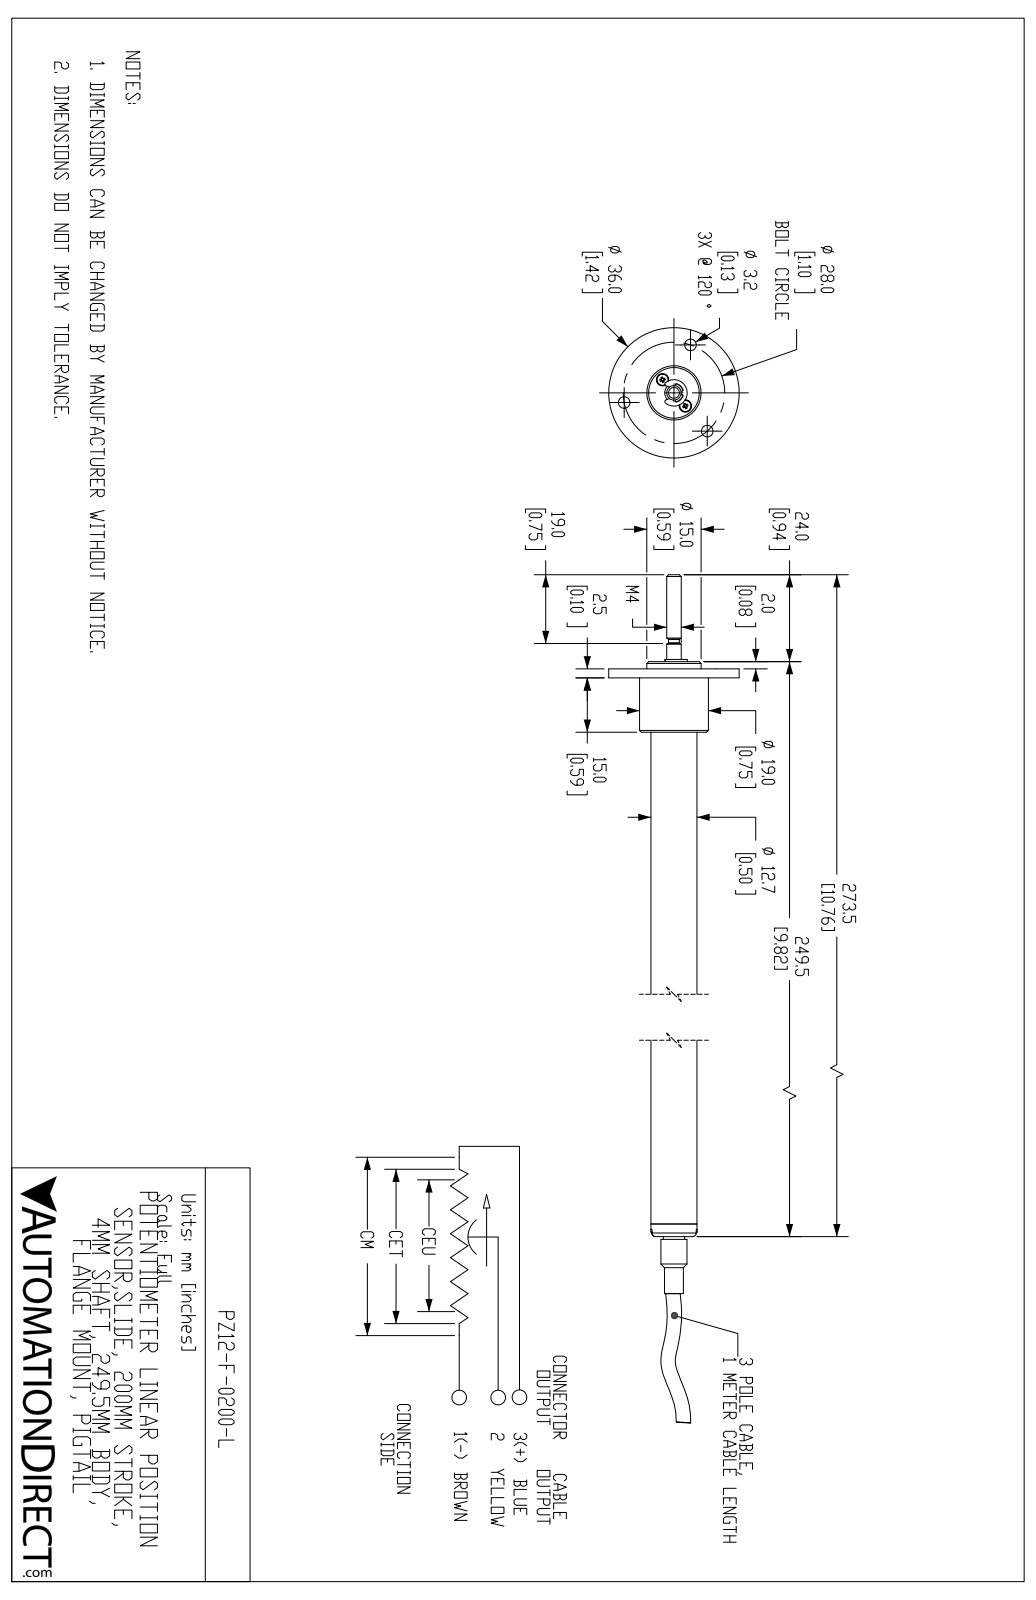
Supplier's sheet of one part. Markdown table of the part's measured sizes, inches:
| quantity | value |
| --- | --- |
| part name | PZ12-F-200-L |
| STEP written by | SolidWorks 2019 (AUTOMOTIVE_DESIGN) |
| units | inches |
| bodies | 11 solids, 489 faces (129 planar, 135 cylindrical, 225 other) |
| overall size | 12.715 × 1.417 × 1.417 |
| volume | 2.384 in³ |
| surface area | 32.86 in² |
| round holes (diameter × count) | 0.126 × 4, 0.055 × 2, 0.079 × 2, 0.134 × 2, 0.039 × 1, 0.138 × 1, 0.201 × 1, 0.236 × 1, 0.502 × 1 |
| round bosses / shafts (diameter × count) | 0.126 × 4, 0.063 × 4, 1.417 × 1, 0.748 × 1, 0.591 × 1, 0.5 × 1, 0.283 × 1, 0.233 × 1 |
| partial cylindrical surfaces (radius × count) | 0.01 × 4, 0.02 × 2, 0.026 × 2, 0.069 × 2, 0.017 × 1, 0.103 × 1, 0.144 × 1 |
| main face-to-face distances | 0.098, 9.429, 9.528, 0.287, 0.079, 0.039, 0.146, 9.606, 0.177, 0.591 |
| hole center spacings | 0.189, 0.551, 0.047, 0.375, 0.485, 0.666, 0.954, 0.362 |
